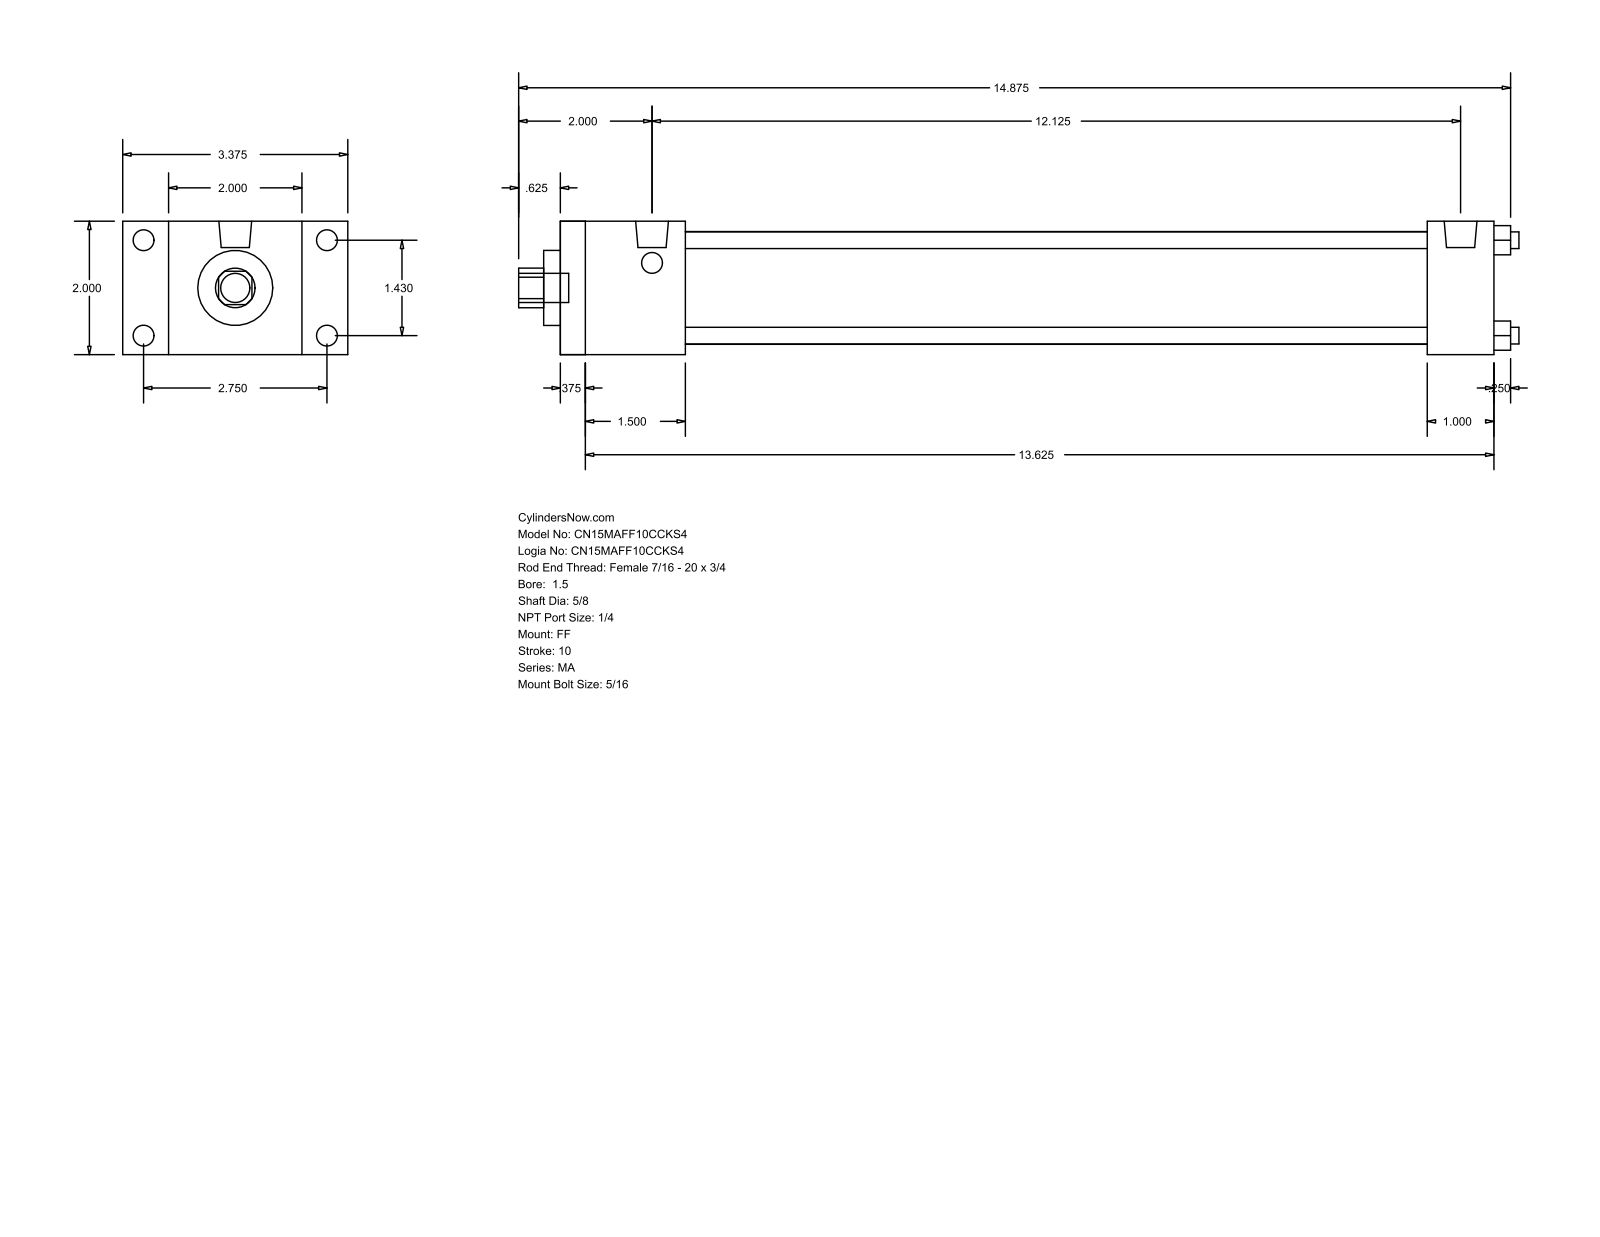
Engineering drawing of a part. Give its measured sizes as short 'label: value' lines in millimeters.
name: MA_FF__0150_0.625
written by: GSSL Pune (CONFIG_CONTROL_DESIGN)
unit: mm
bodies: 0 solids, 92 faces (64 planar, 28 cylindrical, 0 other)
size: 381 × 85.72 × 50.8
holes: 4× ⌀6.35, 1× ⌀15.88, 1× ⌀28.57, 1× ⌀42.93
bosses: 8× ⌀7.94, 2× ⌀12.49, 1× ⌀11.11
rounds: 1× R7.54
face distances: 50.8, 355.6, 9.52, 346.08, 47.62, 330.19, 38.1, 320.67, 282.57, 307.98
hole spacings: 25.68, 36.32, 51.36
